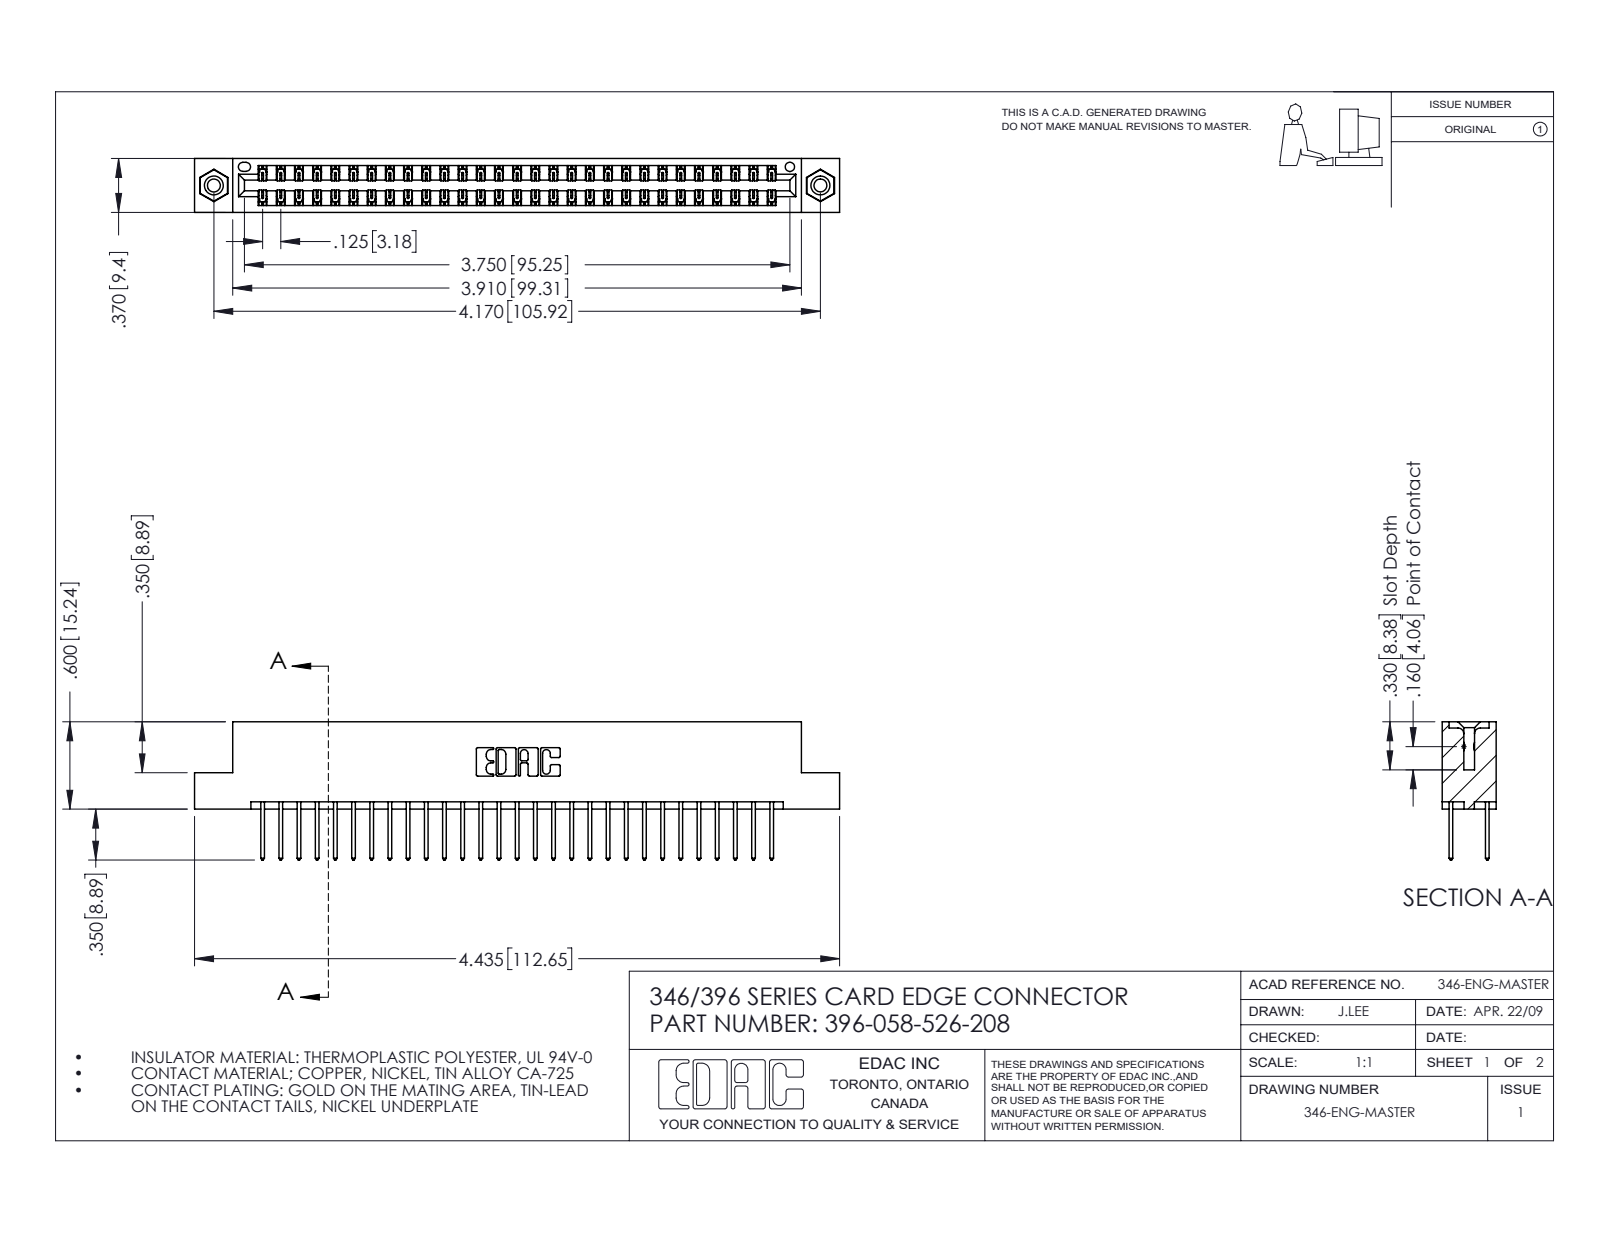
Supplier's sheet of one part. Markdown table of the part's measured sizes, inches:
| quantity | value |
| --- | --- |
| part name | 346 Part_Flush Mounting Lugs - 0.156 Dia-TI; 345-292-001_345-293-126; 396-058-526-208; 345-250-001_345-250-003-102 |
| STEP written by | SolidWorks 2016 (CONFIG_CONTROL_DESIGN) |
| units | inches |
| bodies | 61 solids, 3198 faces (2138 planar, 1044 cylindrical, 16 other) |
| overall size | 4.435 × 0.95 × 0.37 |
| volume | 0.67 in³ |
| surface area | 23.75 in² |
| round holes (diameter × count) | 0.089 × 2, 0.125 × 2, 0.156 × 2, 0.064 × 1 |
| round bosses / shafts (diameter × count) | 0.155 × 2 |
| partial cylindrical surfaces (radius × count) | 0.006 × 87, 0.01 × 58, 0.01 × 22, 0.007 × 6, 0.031 × 6, 0.026 × 3, 0.014 × 2, 0.022 × 2 |
| main face-to-face distances | 0.048, 0.322, 0.25, 0.37, 0.072, 0.298, 0.025, 0.275, 0.148, 0.222 |
| hole center spacings | 0.246, 3.962, 4.17 |
